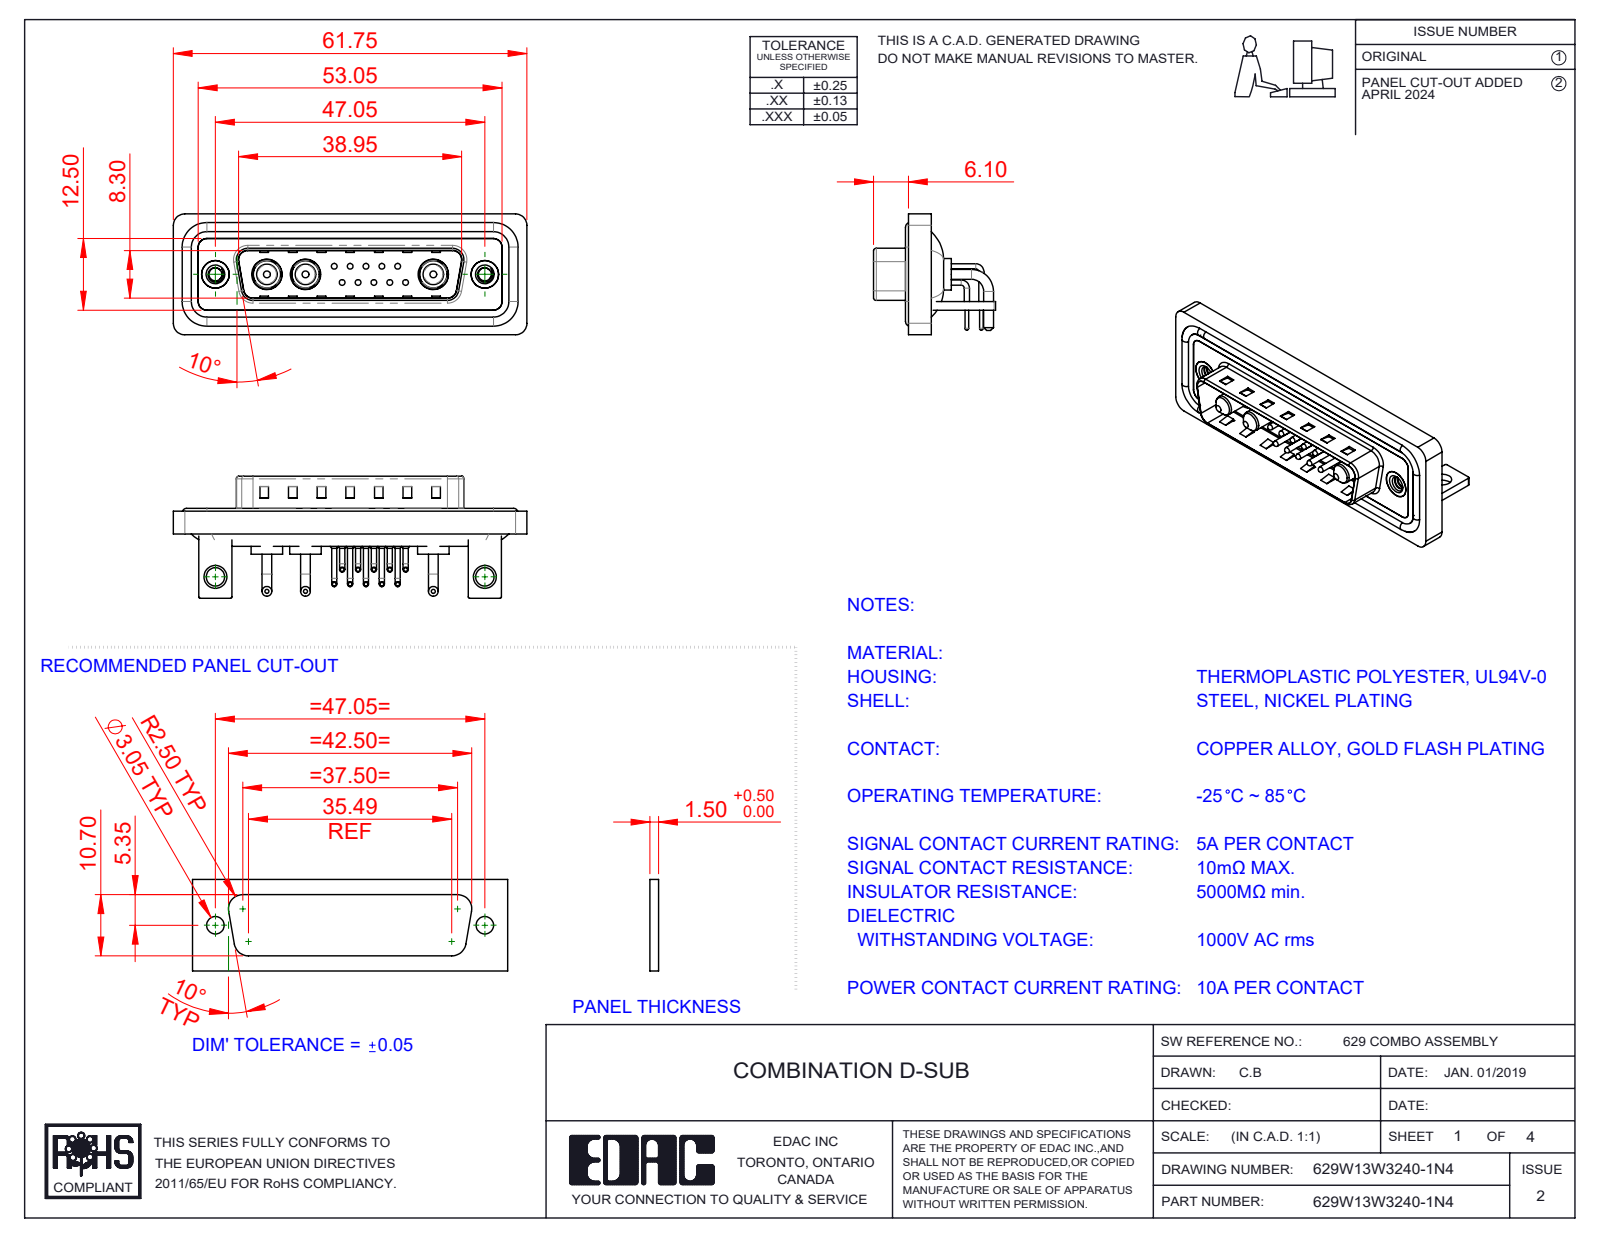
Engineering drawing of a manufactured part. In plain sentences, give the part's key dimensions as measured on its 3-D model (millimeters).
The part is named "629Combo Housing_13W3; 629Combo Contact Row 1; 629Combo Stabilizer Bracket; 629Combo Shell Rear_25 Contacts (+6 more)". Its 3-D file was written by "SolidWorks 2023 (CONFIG_CONTROL_DESIGN)". It is 25 solids with 1752 faces: 899 planar, 629 cylindrical and 224 other. Overall it measures 61.75 by 21.3 by 21.1 millimeters. Its volume is 7 714 cubic millimeters and its surface area 12 930 square millimeters. Round holes: 10 of diameter 0.75, 10 of diameter 1.6, 10 of diameter 2, 3 of diameter 4.85, 3 of diameter 5.3, 2 of diameter 2.26, 2 of diameter 3.2, 2 of diameter 4, 2 of diameter 4.8, 2 of diameter 5. Round bosses or shafts: 20 of diameter 0.9, 10 of diameter 1.5, 10 of diameter 1, 10 of diameter 0.65, 6 of diameter 1.7, 4 of diameter 1.6, 3 of diameter 5.5, 3 of diameter 5.2. Partial cylindrical surfaces (rounded edges, fillets, slot ends): 19 of radius 2, 18 of radius 1.5, 16 of radius 0.25, 10 of radius 1.01, 9 of radius 0.5, 8 of radius 1.6, 4 of radius 0.6, 4 of radius 0.65. The main face-to-face distances are 0.4, 1.5, 0.8, 2.9, 2.1, 1.1, 4.1, 1.6, 3.7, 4.5. The hole center spacings are 3.16, 2.77, 5.04, 5.54, 7.49, 5.03, 8.31, 10.11.
